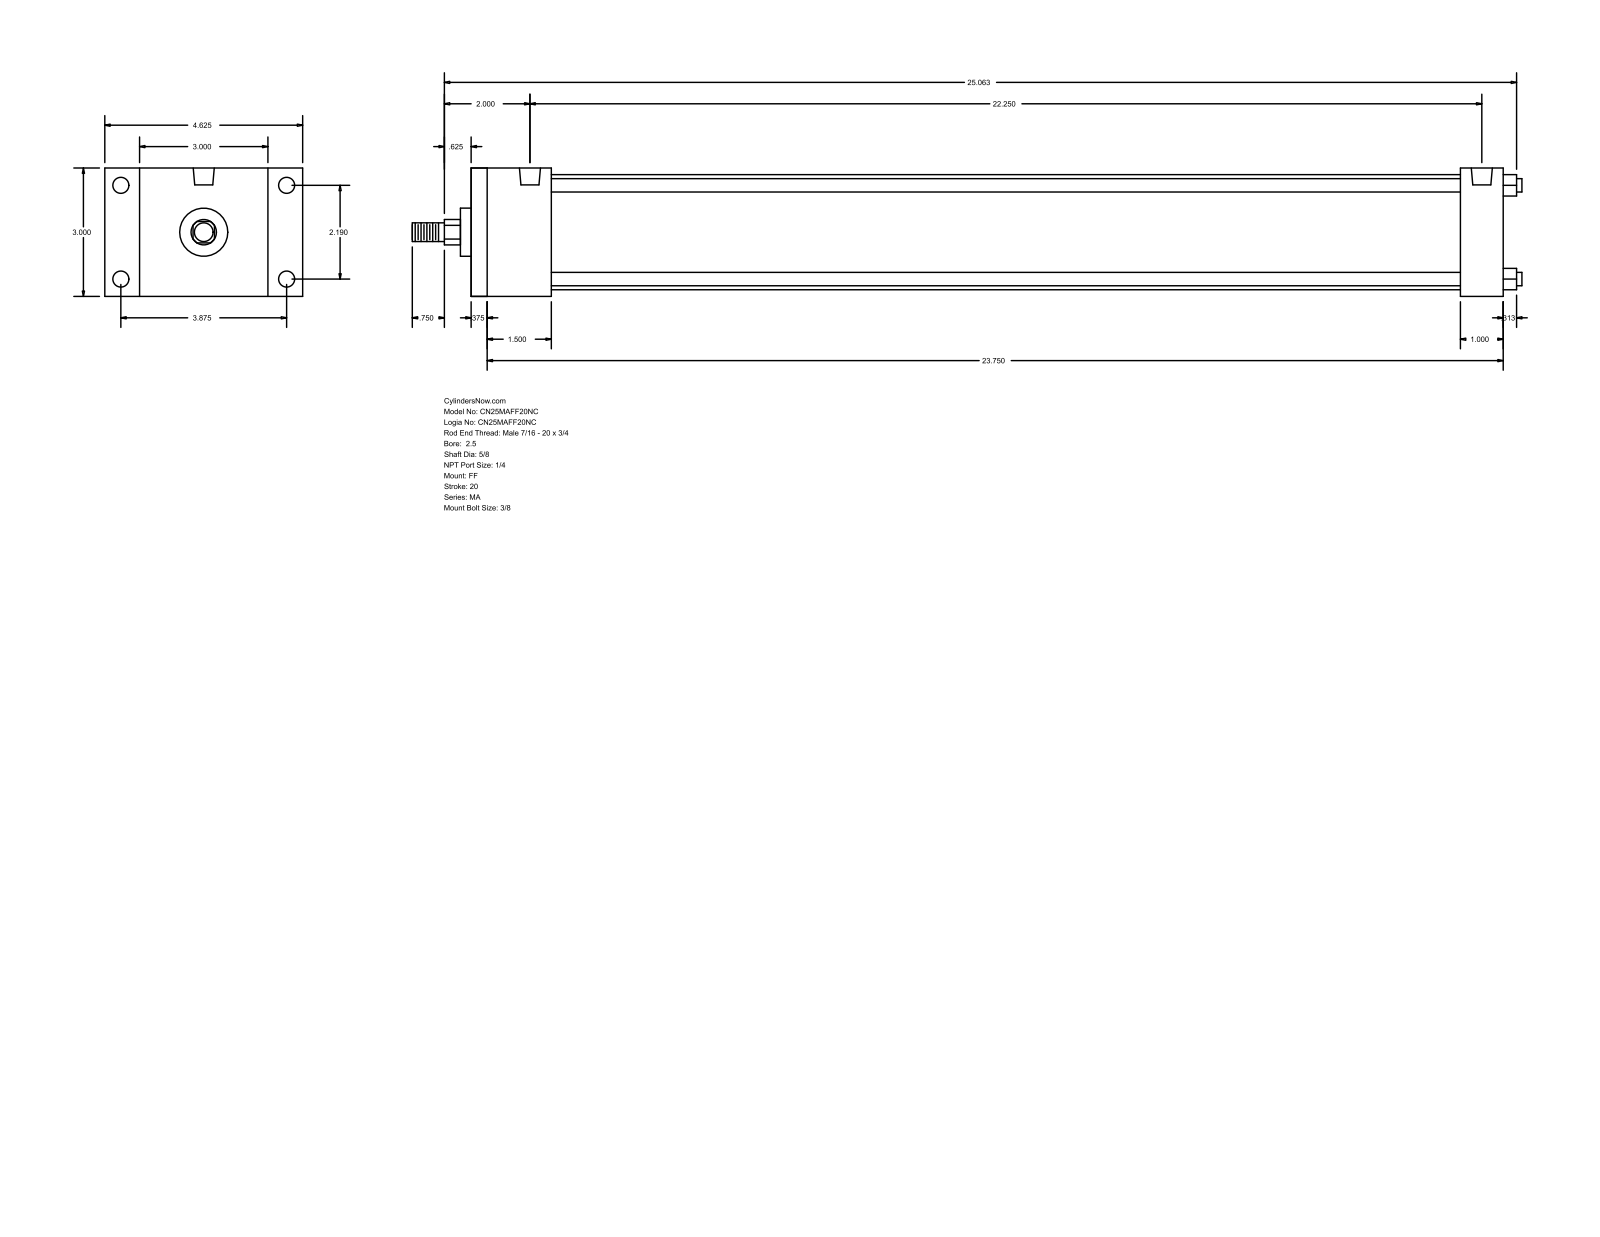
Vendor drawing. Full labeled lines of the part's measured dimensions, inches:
Part name (STEP PRODUCT): MA_FF__0250_0.625
STEP written by: GSSL Pune (CONFIG_CONTROL_DESIGN)
Units: inches
Bodies: 0 solids, 92 faces (64 planar, 28 cylindrical, 0 other)
Overall size (bounding box): 25.937 × 4.625 × 3
Round holes (diameter × count): ⌀0.313 ×4, ⌀0.375 ×4, ⌀0.492 ×2
Round bosses / shafts (diameter × count): ⌀0.313 ×4, ⌀2.69 ×1, ⌀1.125 ×1, ⌀0.625 ×1, ⌀0.437 ×1
Partial cylindrical surfaces — rounded edges, fillets, slot ends (radius × count): R0.297 ×1
Main face-to-face distances: 3, 24.125, 23.75, 0.375, 1, 1.875, 23.125, 1.5, 22.75, 21.25
Hole centre spacings: 2.19, 3.875, 4.451, 22.25
